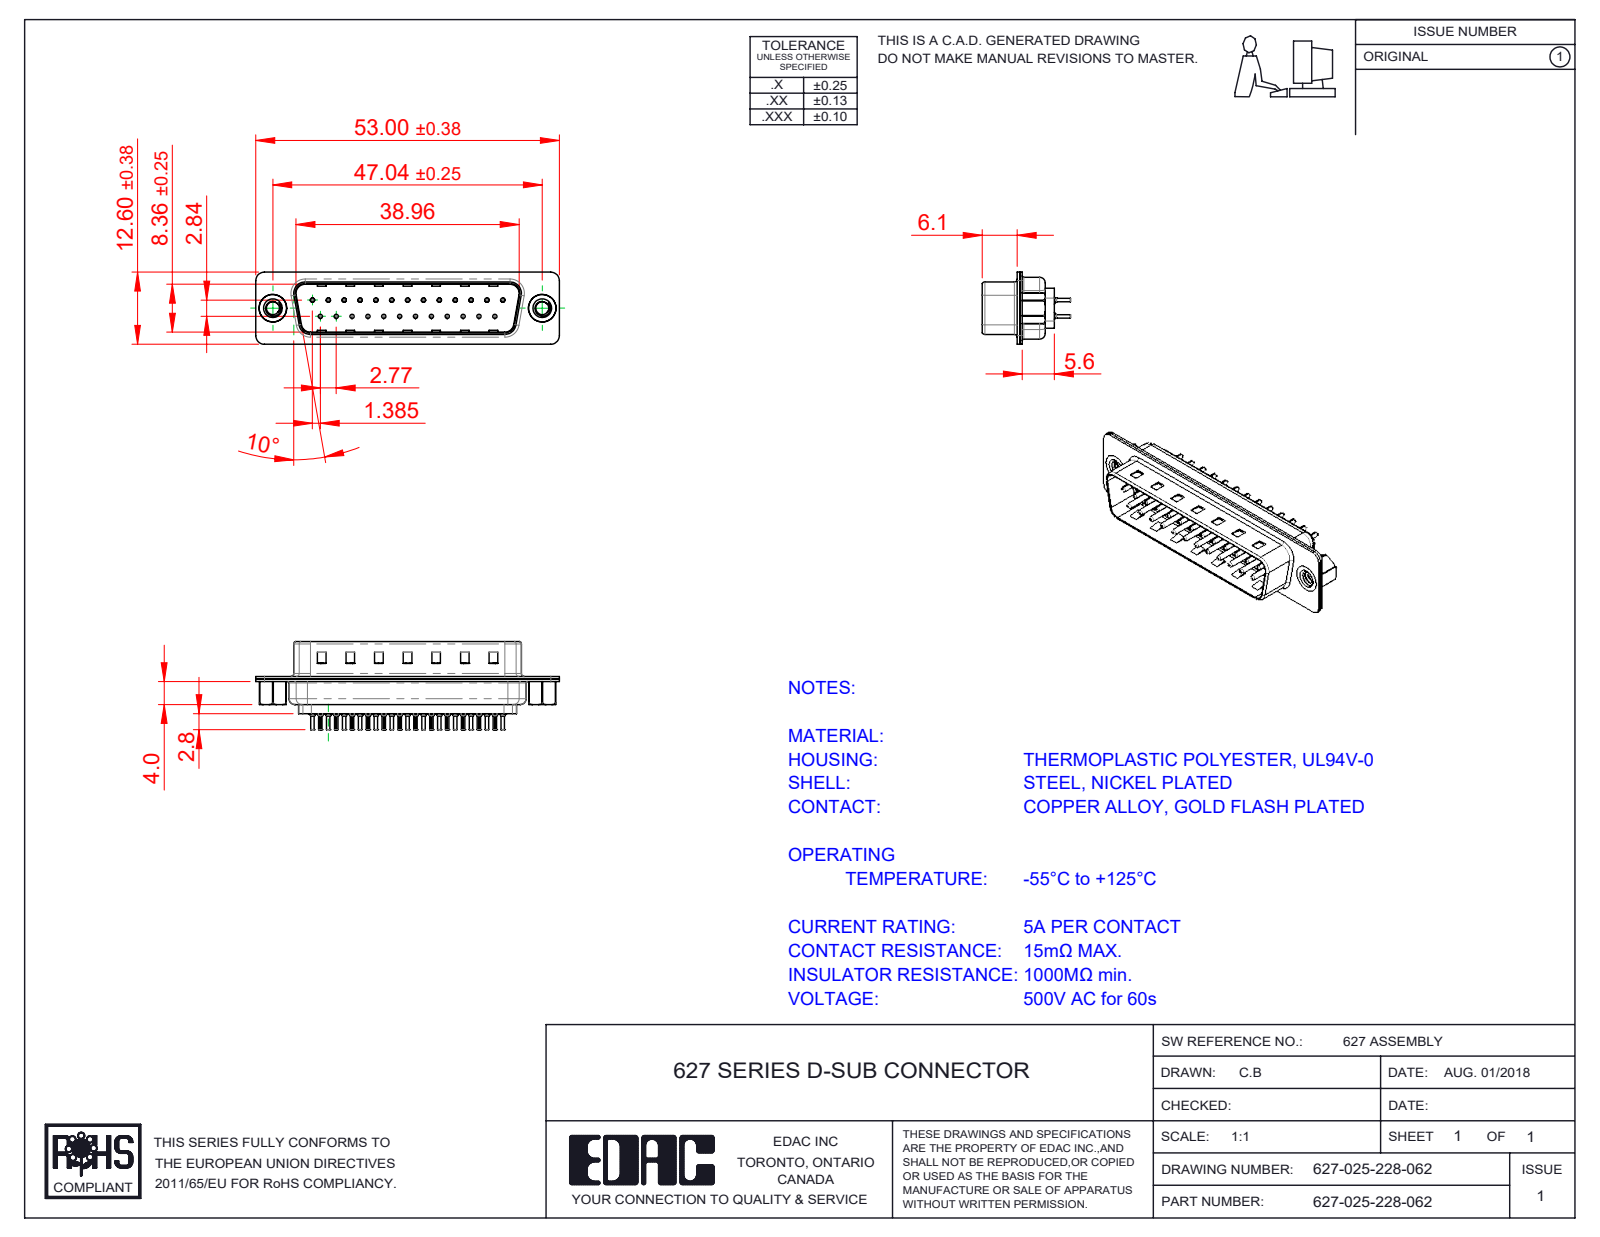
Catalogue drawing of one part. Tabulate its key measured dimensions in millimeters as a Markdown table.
| quantity | value |
| --- | --- |
| part name | 627 4-40 Threaded Rivet; 627 Contact Row 2_28L; 627 Housing_25 FF; 627 Shell Front_25 Contacts (+3 more) |
| STEP written by | SolidWorks 2020 (CONFIG_CONTROL_DESIGN) |
| units | millimeters |
| bodies | 31 solids, 2883 faces (777 planar, 1115 cylindrical, 991 other) |
| overall size | 53 × 18.8 × 12.6 |
| volume | 3 273 mm³ |
| surface area | 8 914 mm² |
| round holes (diameter × count) | 0.2 × 25, 0.35 × 25, 1.1 × 25, 1.6 × 25, 2.26 × 2, 4 × 2, 4.8 × 2 |
| round bosses / shafts (diameter × count) | 2 × 25, 1.5 × 25, 0.75 × 25, 0.6 × 25, 5 × 2, 4.9 × 2 |
| partial cylindrical surfaces (radius × count) | 0.1 × 50, 1.5 × 16, 2 × 12, 0.5 × 8, 1.6 × 8, 0.25 × 4, 0.6 × 4, 0.65 × 4 |
| main face-to-face distances | 0.4, 0.45, 6.05, 0.82, 9.58, 8.4, 1.5, 0.68, 7.68, 0.9 |
| hole center spacings | 3.16, 2.77, 5.54, 8.31, 11.08, 13.85, 5.04, 7.49 |
